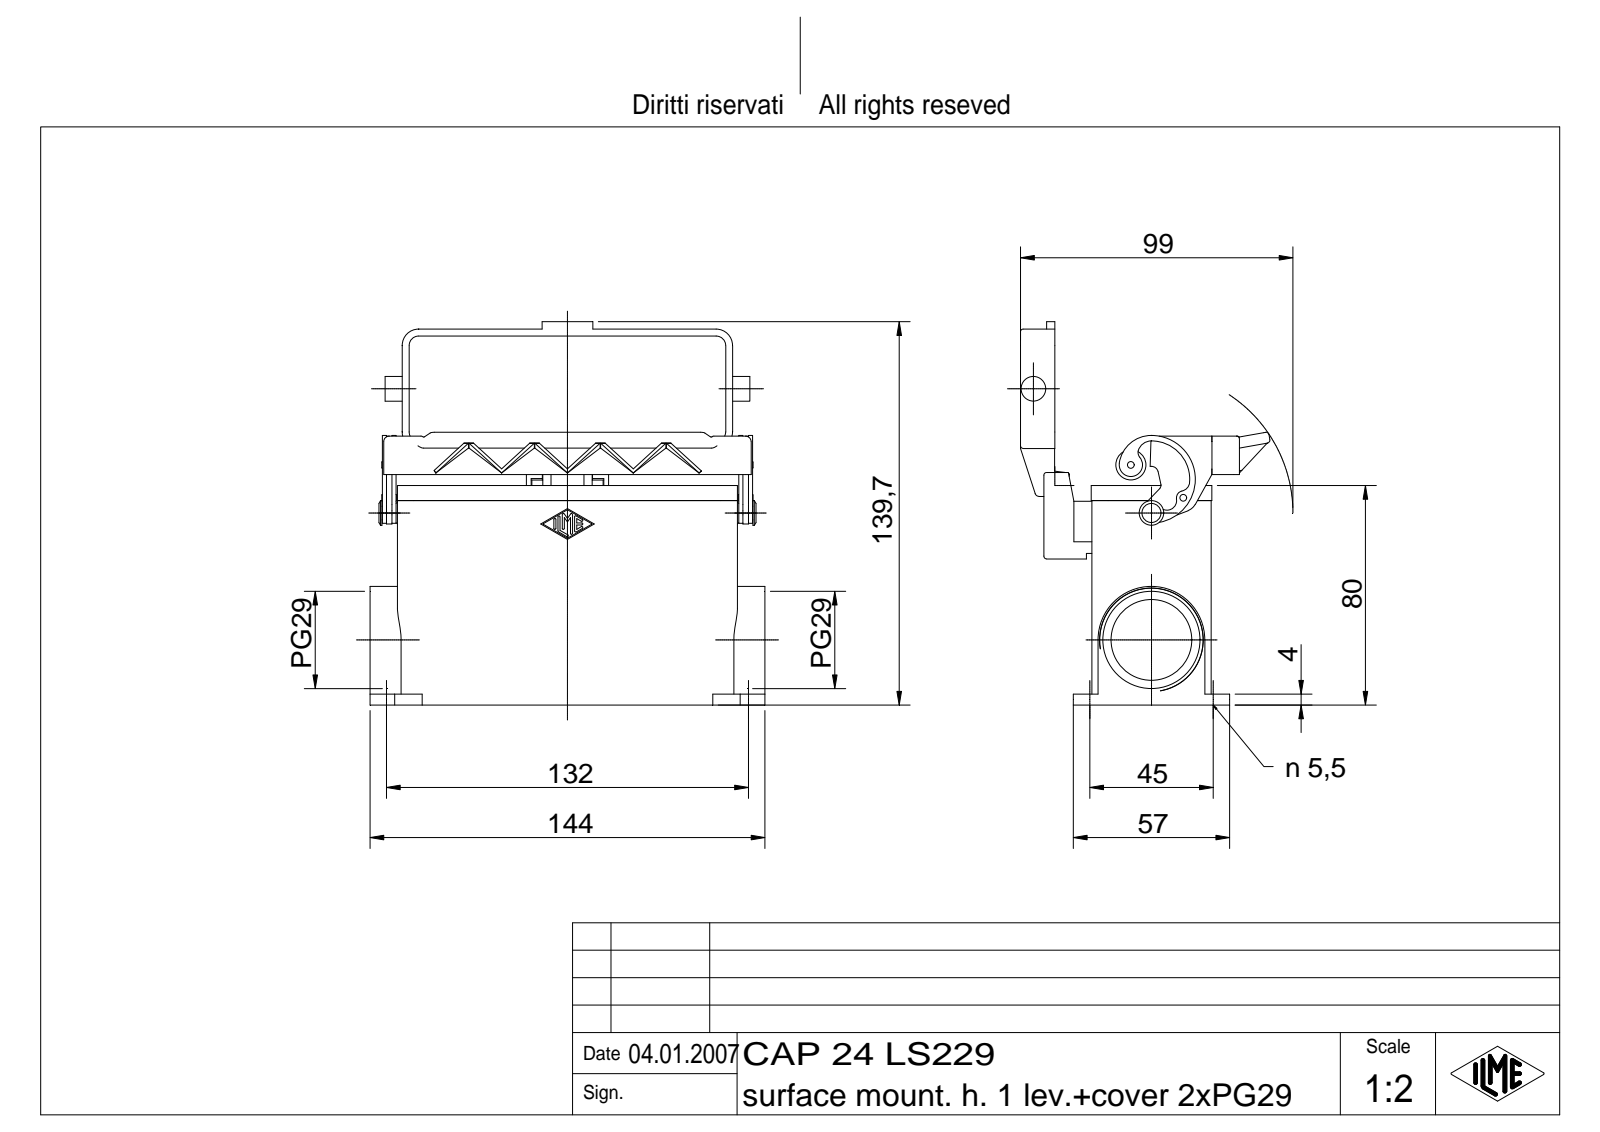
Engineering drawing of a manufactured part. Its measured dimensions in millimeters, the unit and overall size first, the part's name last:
Units: millimetres
Overall size (bounding box): 144 × 139.7 × 90.95
Round holes (diameter × count): ⌀5.5 ×4, ⌀2 ×1, ⌀4 ×1, ⌀29.48 ×1, ⌀35.48 ×1
Round bosses / shafts (diameter × count): ⌀9 ×2, ⌀5 ×2, ⌀11 ×1, ⌀7 ×1, ⌀4 ×1, ⌀3 ×1, ⌀2.5 ×1
Partial cylindrical surfaces — rounded edges, fillets, slot ends (radius × count): R1 ×18, R0.38 ×14, R2 ×12, R6 ×12, R1.5 ×6, R3.5 ×6, R3 ×4, R0.5 ×3
Main face-to-face distances: 3, 40.5, 43.5, 4, 37.5, 26, 66.5, 69.5, 29, 25.5
Hole centre spacings: 45, 132, 139.46, 53.04
Volume: 185 264 mm³ · Surface area: 105 982 mm²
Bodies: 6 solids, 628 faces (282 planar, 182 cylindrical, 164 other)
Part name (STEP PRODUCT): CAP 24 LS229
STEP written by: Autodesk Inventor 7 (AUTOMOTIVE_DESIGN)
